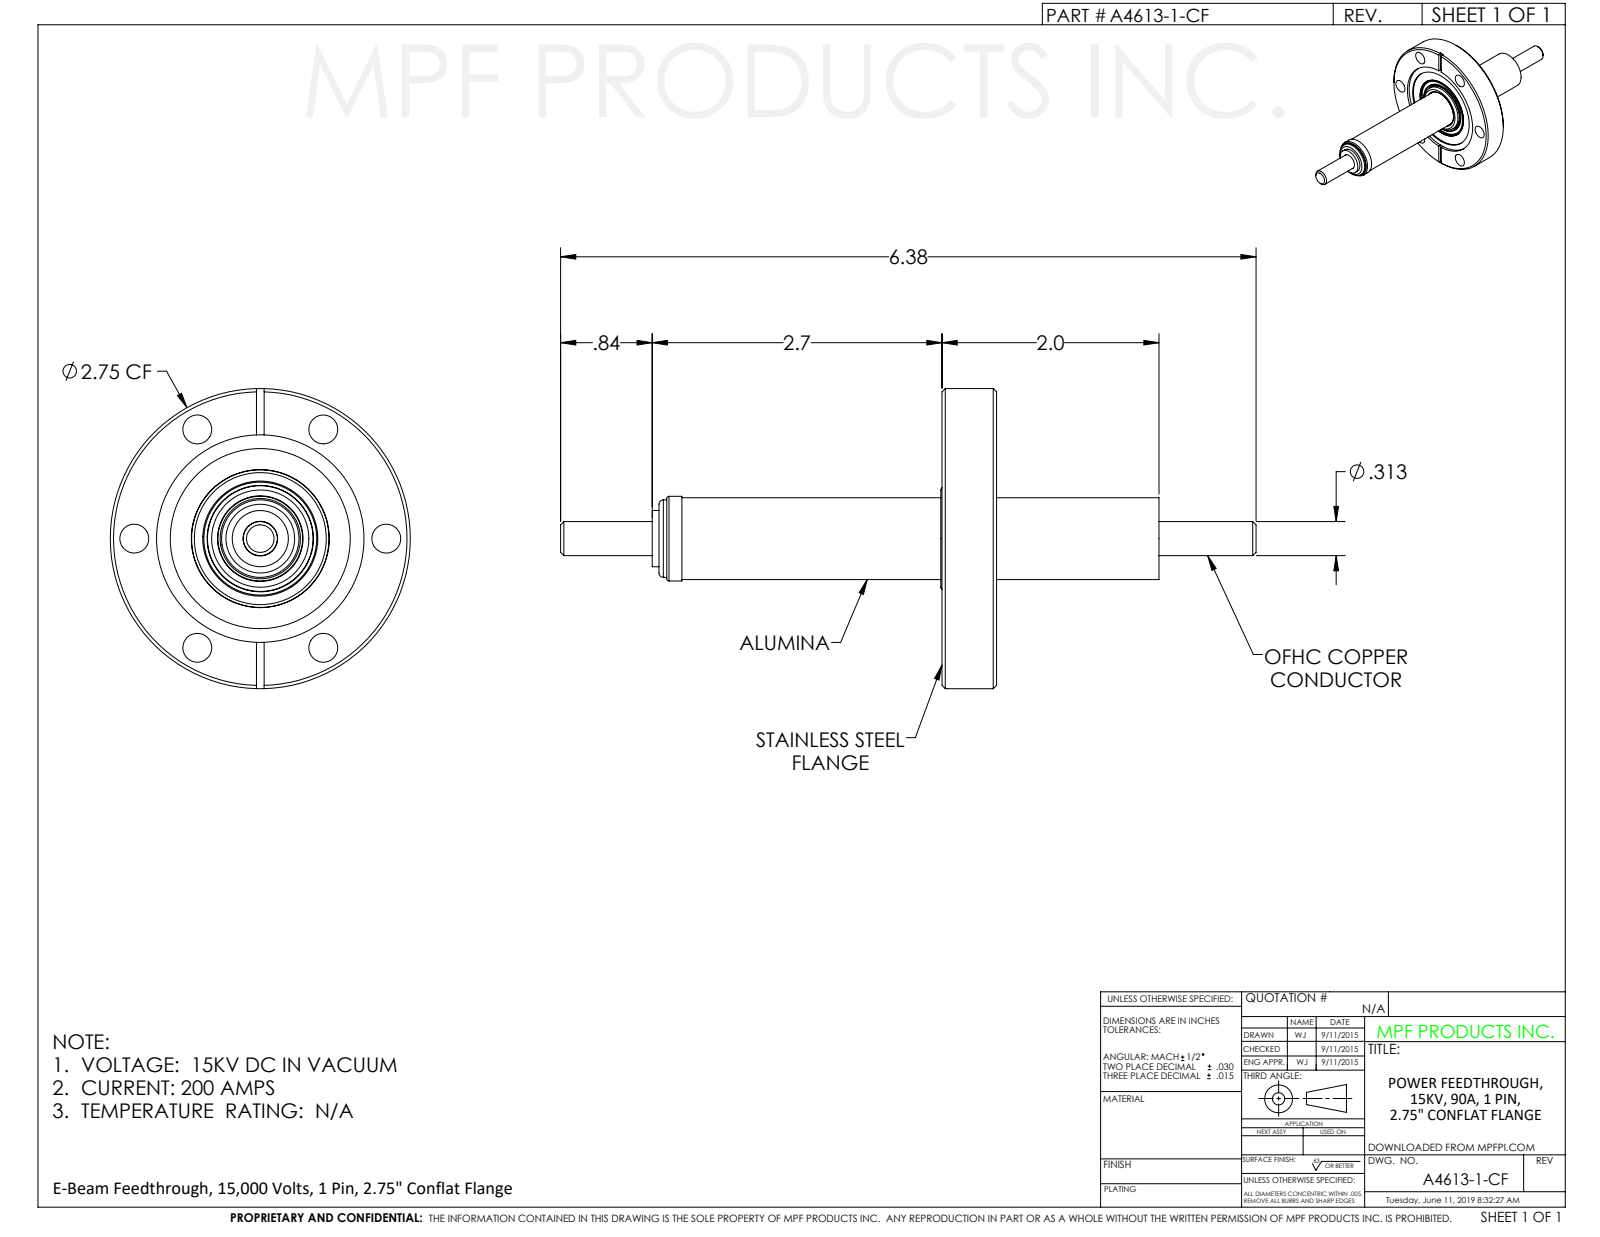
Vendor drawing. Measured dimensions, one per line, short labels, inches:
name: A4613-1-CF
written by: SolidWorks 2019 (CONFIG_CONTROL_DESIGN)
unit: in
bodies: 1 solid, 73 faces (19 planar, 36 cylindrical, 18 other)
size: 6.375 × 2.75 × 2.75
volume: 4.628 in³; area: 31.4 in²
holes: 6× ⌀0.265, 1× ⌀1.265, 1× ⌀1.65, 1× ⌀1.902
bosses: 1× ⌀2.75, 1× ⌀0.776, 1× ⌀0.75, 1× ⌀0.71, 1× ⌀0.515, 1× ⌀0.313
face distances: 0.5, 0.449, 0.051, 0.349, 0.1, 0.151, 0.35, 0.099, 0.15, 1.489
hole spacings: 1.155, 2.001, 2.31
